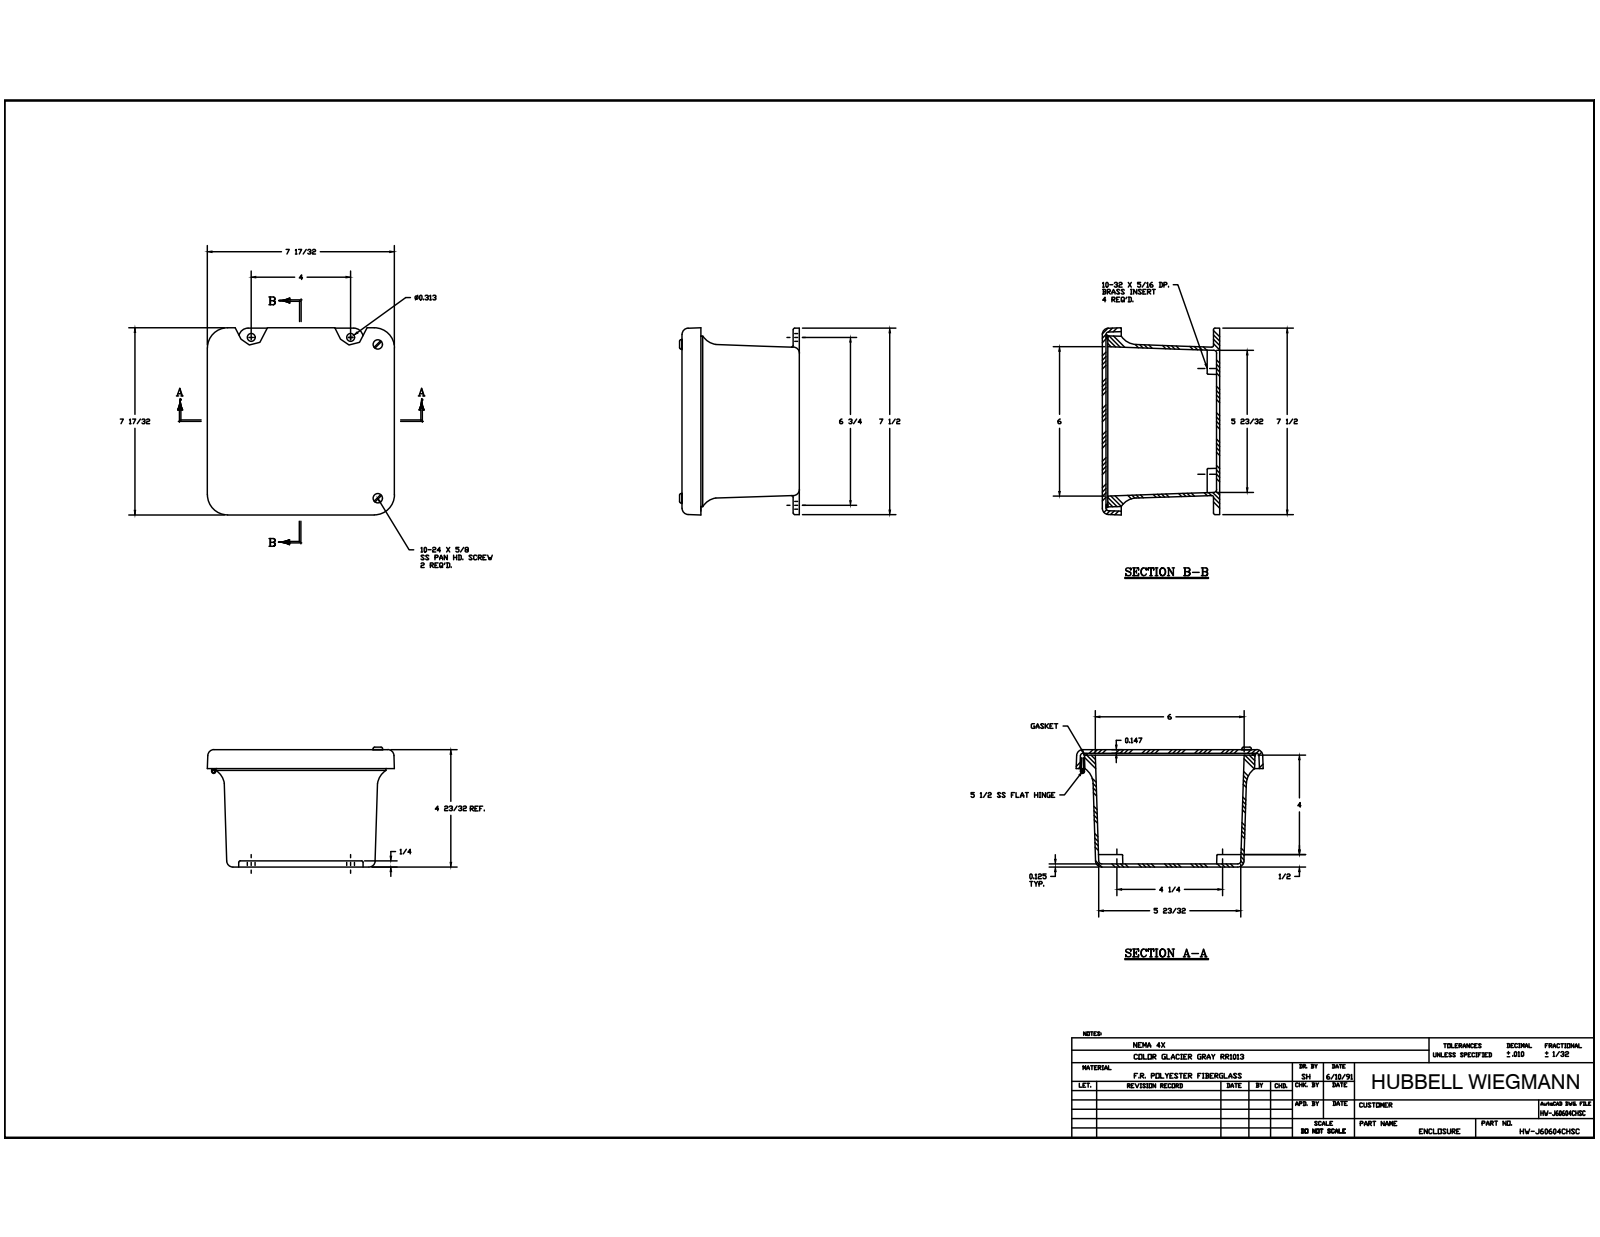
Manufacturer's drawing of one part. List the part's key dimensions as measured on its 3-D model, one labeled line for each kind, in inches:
Part name (STEP PRODUCT): J606HW_4; RMINS45821P_163; RMINS45821P_164; RMINS45821P_165 (+8 more)
STEP written by: Autodesk Inventor 2014 (AUTOMOTIVE_DESIGN)
Units: inches
Bodies: 19 solids, 657 faces (200 planar, 251 cylindrical, 206 other)
Overall size (bounding box): 7.553 × 7.525 × 4.972
Volume: 37.79 in³ · Surface area: 502.5 in²
Round holes (diameter × count): ⌀0.131 ×5, ⌀0.14 ×5, ⌀0.152 ×5, ⌀0.156 ×4, ⌀0.218 ×4, ⌀0.145 ×2, ⌀0.085 ×1
Round bosses / shafts (diameter × count): ⌀0.27 ×6, ⌀0.25 ×5, ⌀0.125 ×5, ⌀0.19 ×2, ⌀0.156 ×2, ⌀0.155 ×1
Partial cylindrical surfaces — rounded edges, fillets, slot ends (radius × count): R0.031 ×20, R0.25 ×12, R0.125 ×8, R0.2 ×7, R0.063 ×4, R0.375 ×4, R0.75 ×4, R0.063 ×2
Main face-to-face distances: 0.147, 4.693, 4.841, 0.125, 4.569, 4.716, 0.152, 4.5, 0.216, 4.625
Hole centre spacings: 5.308, 1.37, 2.5, 4.25, 6.187, 7.38, 0.5, 2
